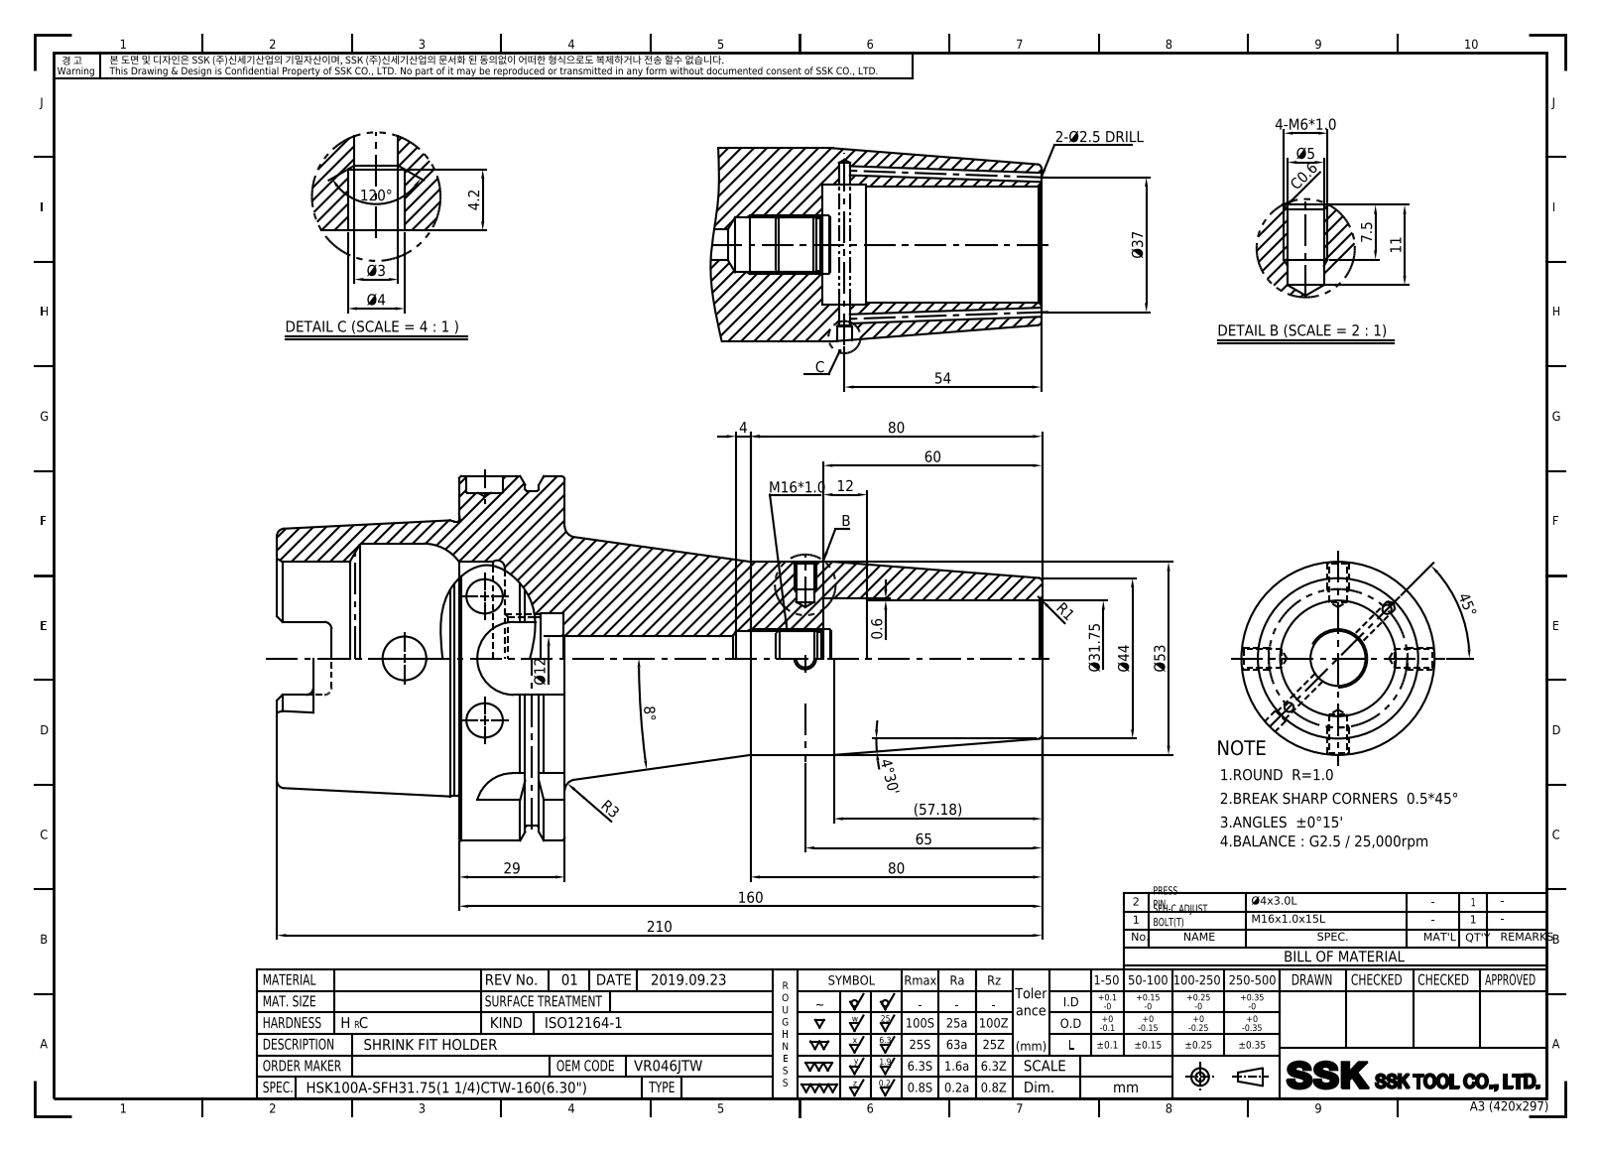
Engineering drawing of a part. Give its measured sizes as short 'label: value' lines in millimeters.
name: LO-HSK100A-SFH31.75CTW-160
written by: Autodesk Inventor 2022 (AUTOMOTIVE_DESIGN)
unit: mm
bodies: 1 solid, 120 faces (38 planar, 37 cylindrical, 45 other)
size: 210 × 100 × 100
volume: 497 366 mm³; area: 79 503 mm²
holes: 2× ⌀2, 2× ⌀12, 1× ⌀10, 1× ⌀14.92, 1× ⌀22.38, 1× ⌀25, 1× ⌀32, 1× ⌀33.2, 1× ⌀53, 1× ⌀63
bosses: 1× ⌀100, 1× ⌀92, 1× ⌀75.41
rounds: 6× R2, 4× R4.88, 4× R10
face distances: 29, 12.5, 16.5, 62.5, 50, 79, 150, 100, 87.5, 71
